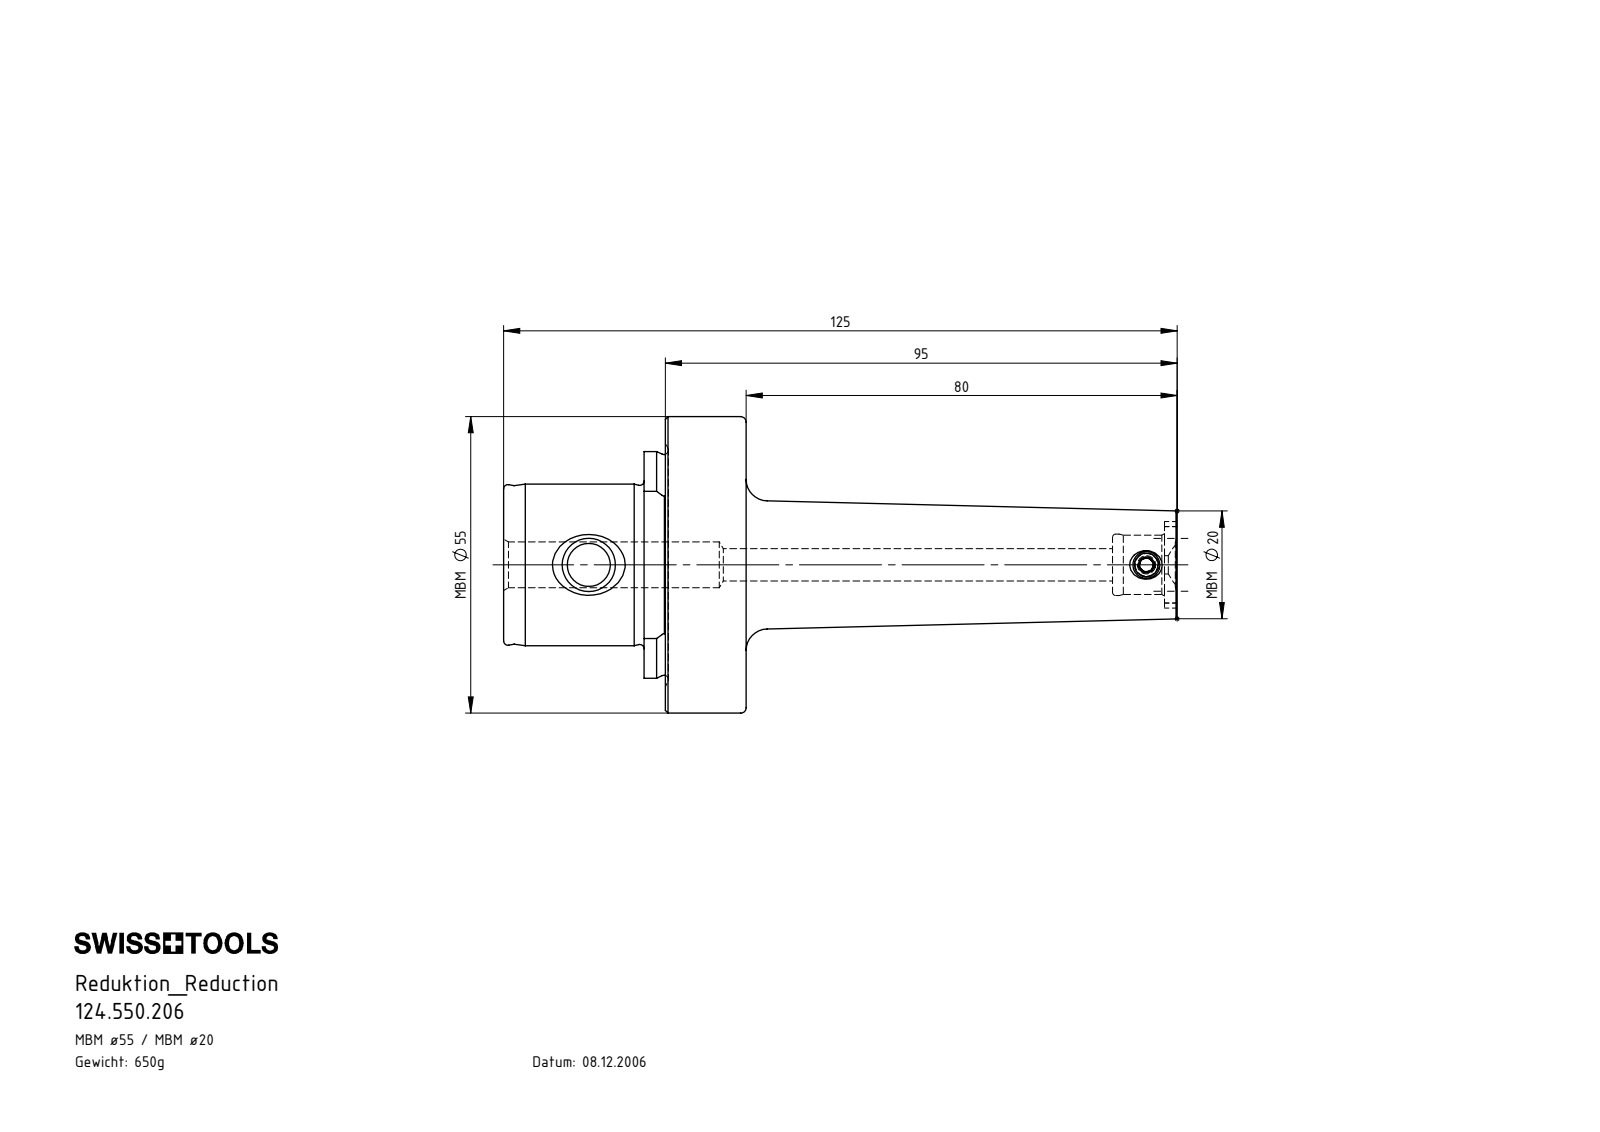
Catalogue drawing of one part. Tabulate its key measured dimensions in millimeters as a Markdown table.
| quantity | value |
| --- | --- |
| part name | 124.550.206; MB5-MB1.K01.095_C; MB1-ER1.001.006_A |
| STEP written by | SolidWorks 2017 (CONFIG_CONTROL_DESIGN) |
| units | millimeters |
| bodies | 2 solids, 139 faces (31 planar, 34 cylindrical, 74 other) |
| overall size | 125 × 55 × 55 |
| volume | 82 798 mm³ |
| surface area | 18 605 mm² |
| round holes (diameter × count) | 2.5 × 1, 4.5 × 1, 6 × 1, 8 × 1, 8.5 × 1, 11 × 1, 11.4 × 1 |
| round bosses / shafts (diameter × count) | 55 × 1, 30 × 1, 5 × 1 |
| partial cylindrical surfaces (radius × count) | 2.2 × 4, 6.5 × 1, 8.03 × 1, 21.02 × 1 |
| main face-to-face distances | 15, 30, 45, 26.05, 3.95, 18.95, 29.85, 3.8, 15.15, 32 |
| hole center spacings | 103.5 |
